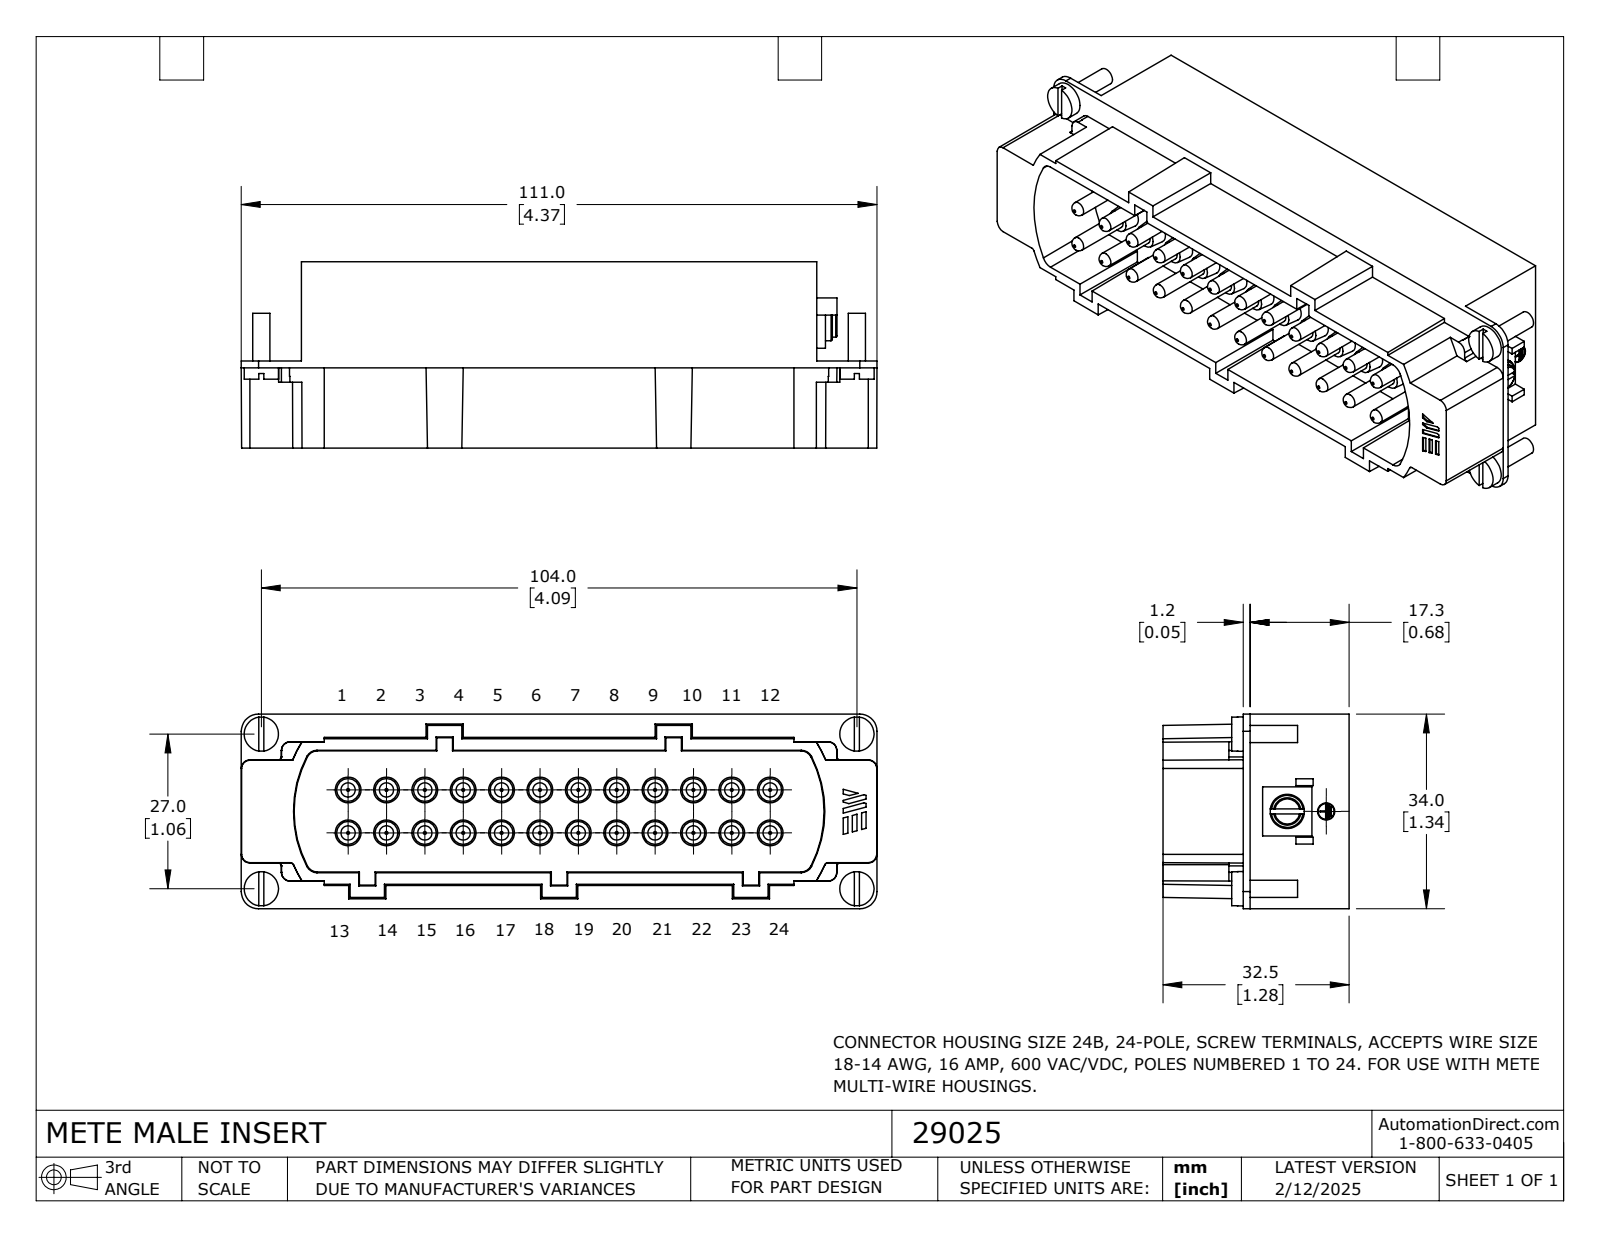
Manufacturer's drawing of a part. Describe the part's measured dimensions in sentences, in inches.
The part is named "29025". Its 3-D file was written by "SolidWorks 2024 (CONFIG_CONTROL_DESIGN)". It is 1 solid with 507 faces: 255 planar, 125 cylindrical and 127 other. Overall it measures 4.37 by 1.339 by 1.28 inches. Its volume is 4.201 cubic inches and its surface area 39.49 square inches. Round holes: 24 of diameter 0.157, 1 of diameter 0.118. Round bosses or shafts: 24 of diameter 0.098, 5 of diameter 0.236, 4 of diameter 0.118, 1 of diameter 0.189, 1 of diameter 0.11. Partial cylindrical surfaces (rounded edges, fillets, slot ends): 4 of radius 0.118. The main face-to-face distances are 0.728, 1.339, 0.551, 1.28, 0.047, 0.681, 0.598, 0.091, 3.543, 0.346. The hole center spacings are 0.264, 0.396, 0.528, 0.605, 0.791, 0.844, 1.055, 1.096.
